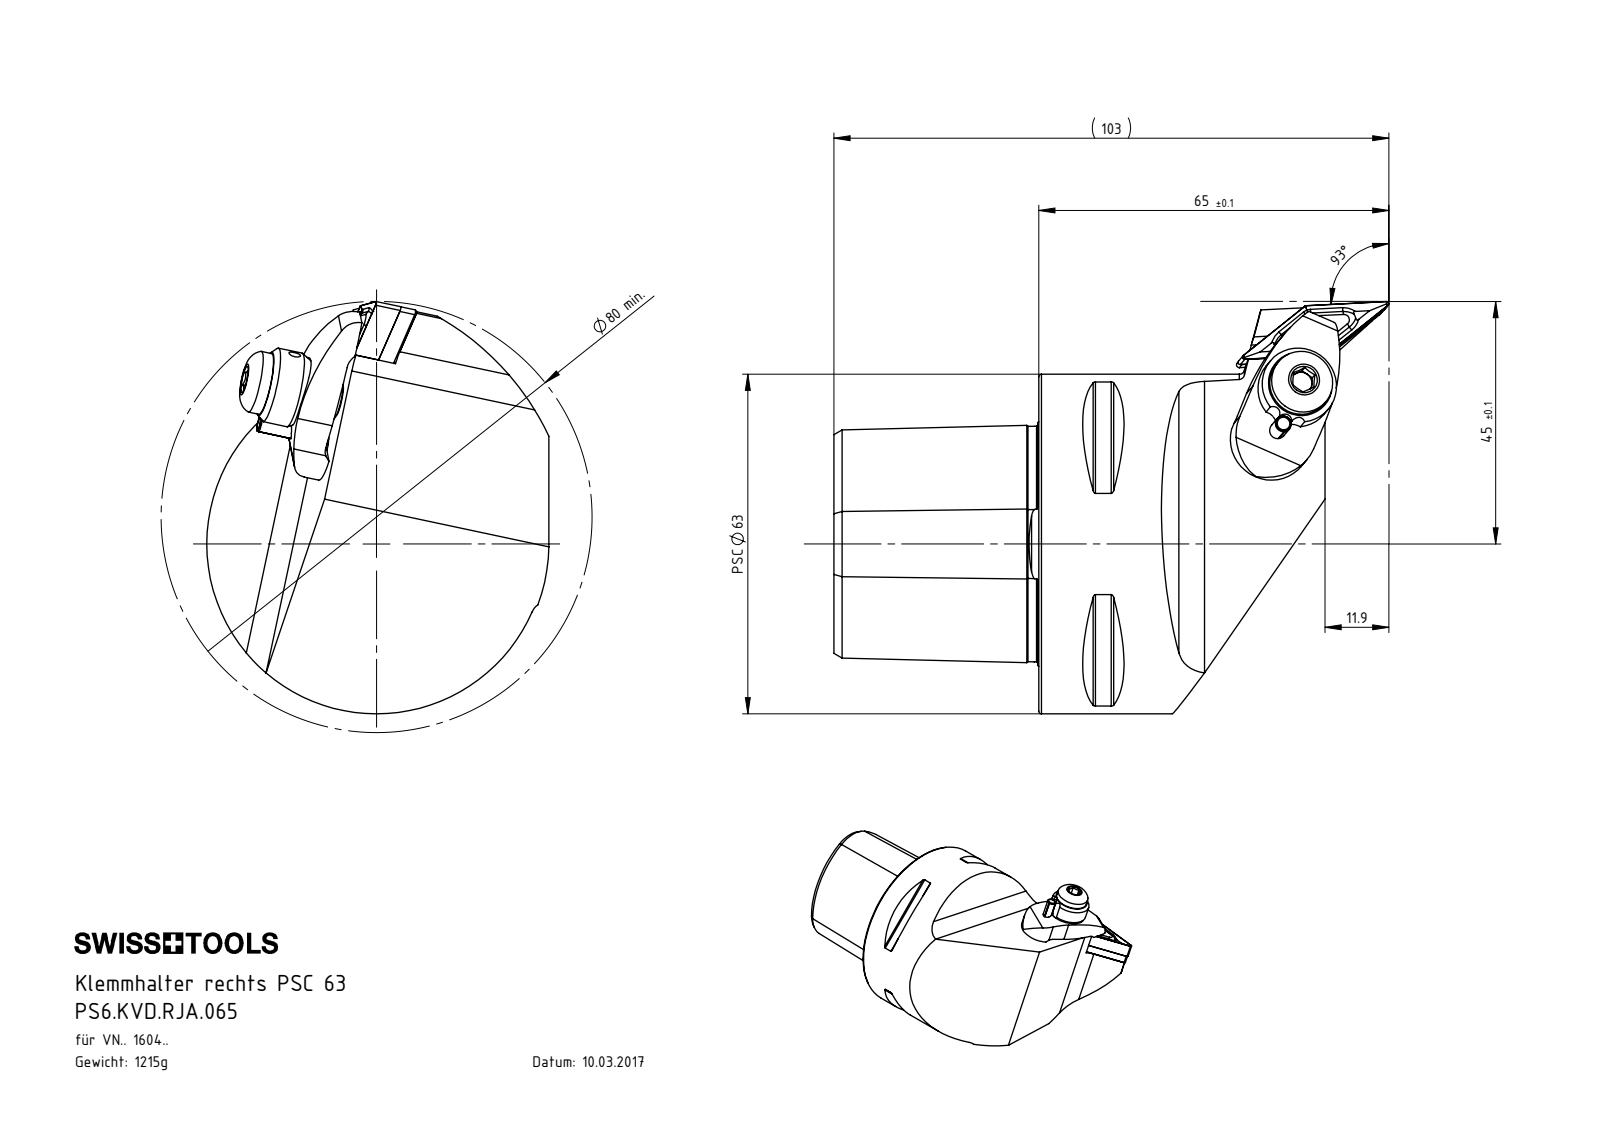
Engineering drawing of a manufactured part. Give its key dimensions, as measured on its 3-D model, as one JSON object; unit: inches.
{"part_name": "WVD-ER2.101.003_A; PS6-KVD.RJA.065; PS6-KVD.RJA.065_A; KVT_MB_600_060 (+7 more)", "step_written_by": "SolidWorks 2015 (CONFIG_CONTROL_DESIGN)", "units": "inches", "bodies": {"solids": 13, "faces": 437, "planar": 106, "cylindrical": 134, "other": 197}, "overall_size": [4.055, 3.012, 2.5], "volume_in3": 9.415, "surface_area_in2": 50, "round_holes": [[0.079, 3], [0.197, 3], [0.276, 2], [0.094, 1], [0.118, 1], [0.13, 1], [0.15, 1], [0.157, 1], [0.195, 1], [0.236, 1], [0.244, 1], [0.272, 1]], "round_bosses_or_shafts": [[0.244, 2], [0.236, 2], [0.118, 2], [2.48, 1], [0.551, 1], [0.453, 1], [0.276, 1], [0.268, 1]], "partial_cylinders_radius": [[0.02, 10], [0.015, 6], [0.016, 4], [0.027, 3], [0.027, 3], [0.059, 3], [0.236, 3], [0.079, 2]], "face_to_face_distances": [1.496, 0.98, 0.175, 0.052, 1.063, 0.433, 0.3, 0.363, 0.226, 0.375], "hole_center_spacings": [0.315, 0.316, 0.322, 0.876, 0.554, 0.556, 0.56, 0.561]}
